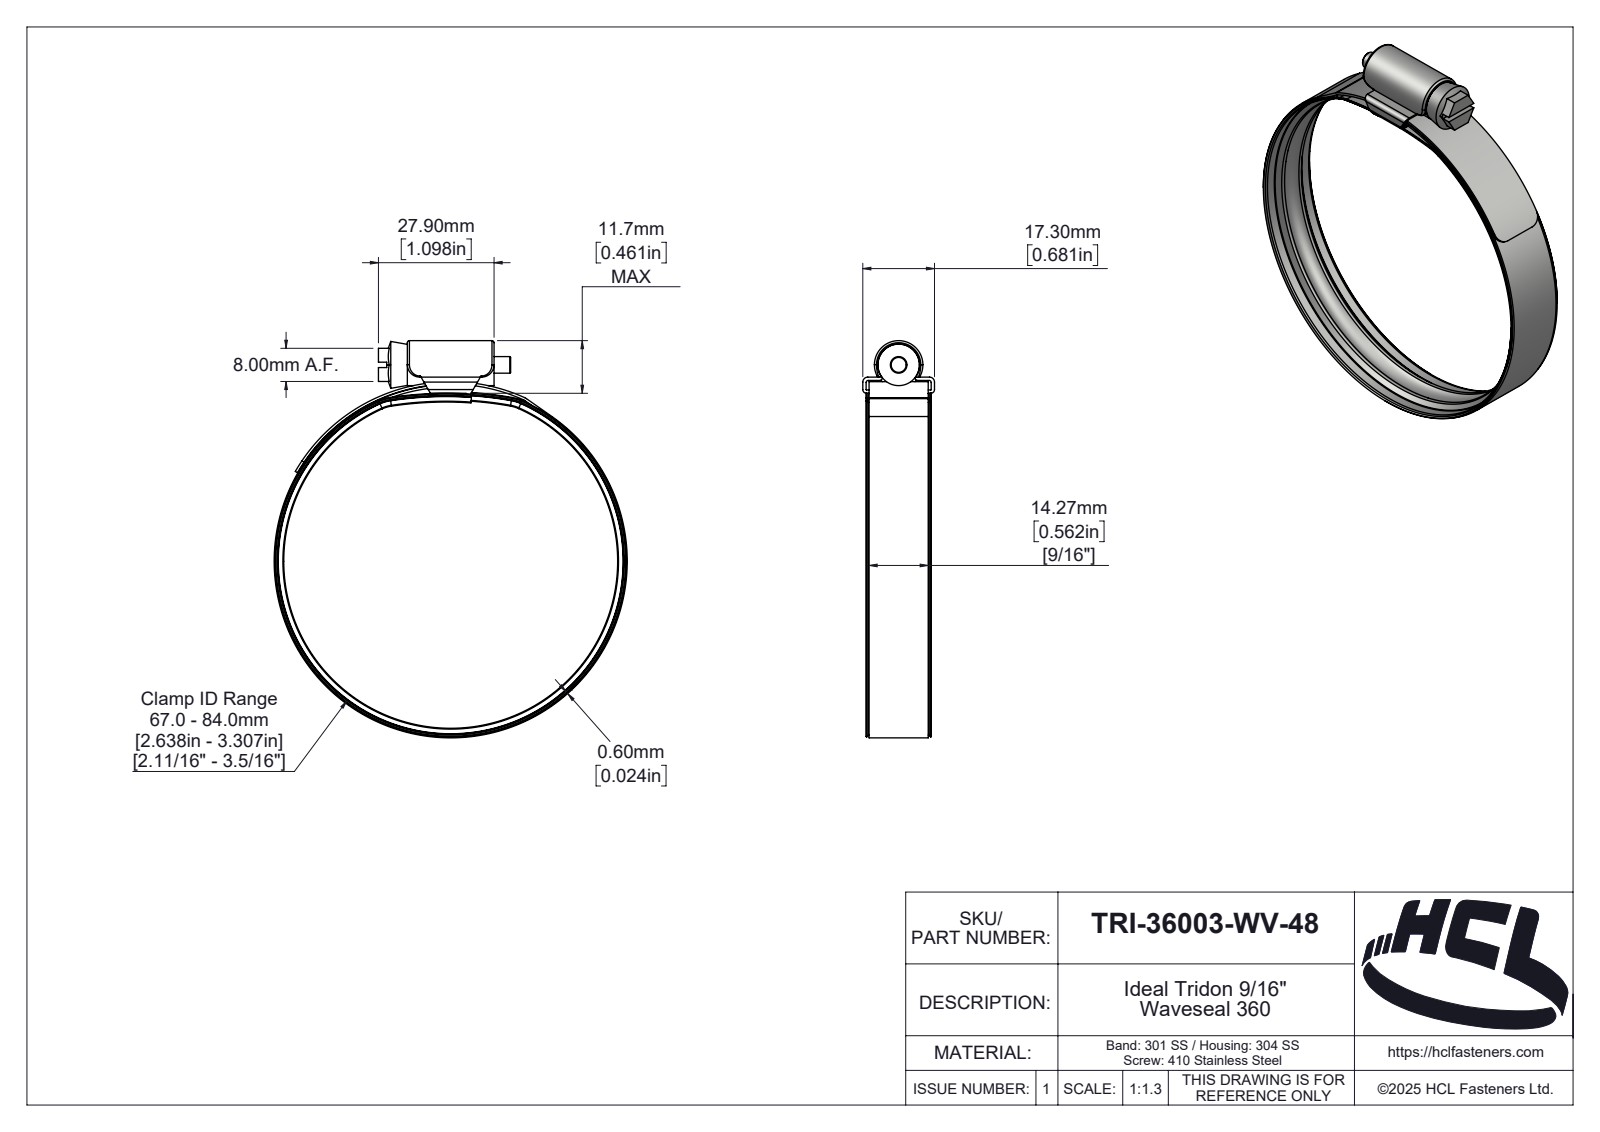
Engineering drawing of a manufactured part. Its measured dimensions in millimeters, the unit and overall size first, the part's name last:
Units: millimetres
Overall size (bounding box): 95.8 × 85.2 × 17.3
Round holes (diameter × count): ⌀83.4 ×1, ⌀84 ×1
Round bosses / shafts (diameter × count): ⌀85.2 ×1, ⌀83.8 ×1, ⌀10 ×1, ⌀4 ×1
Partial cylindrical surfaces — rounded edges, fillets, slot ends (radius × count): R0.5 ×6, R3 ×4, R0.1 ×2, R0.9 ×2, R1.2 ×2, R9.9 ×2, R10.1 ×2, R0.46 ×1
Main face-to-face distances: 0.8, 14.26, 3.1, 0.61, 2.3, 3.9, 27.9, 1.52, 15.78, 16.5
Volume: 6 463 mm³ · Surface area: 21 684 mm²
Bodies: 4 solids, 418 faces (42 planar, 119 cylindrical, 257 other)
Part name (STEP PRODUCT): TRI-36003-WV-48
STEP written by: SolidWorks 2025 (AUTOMOTIVE_DESIGN)
